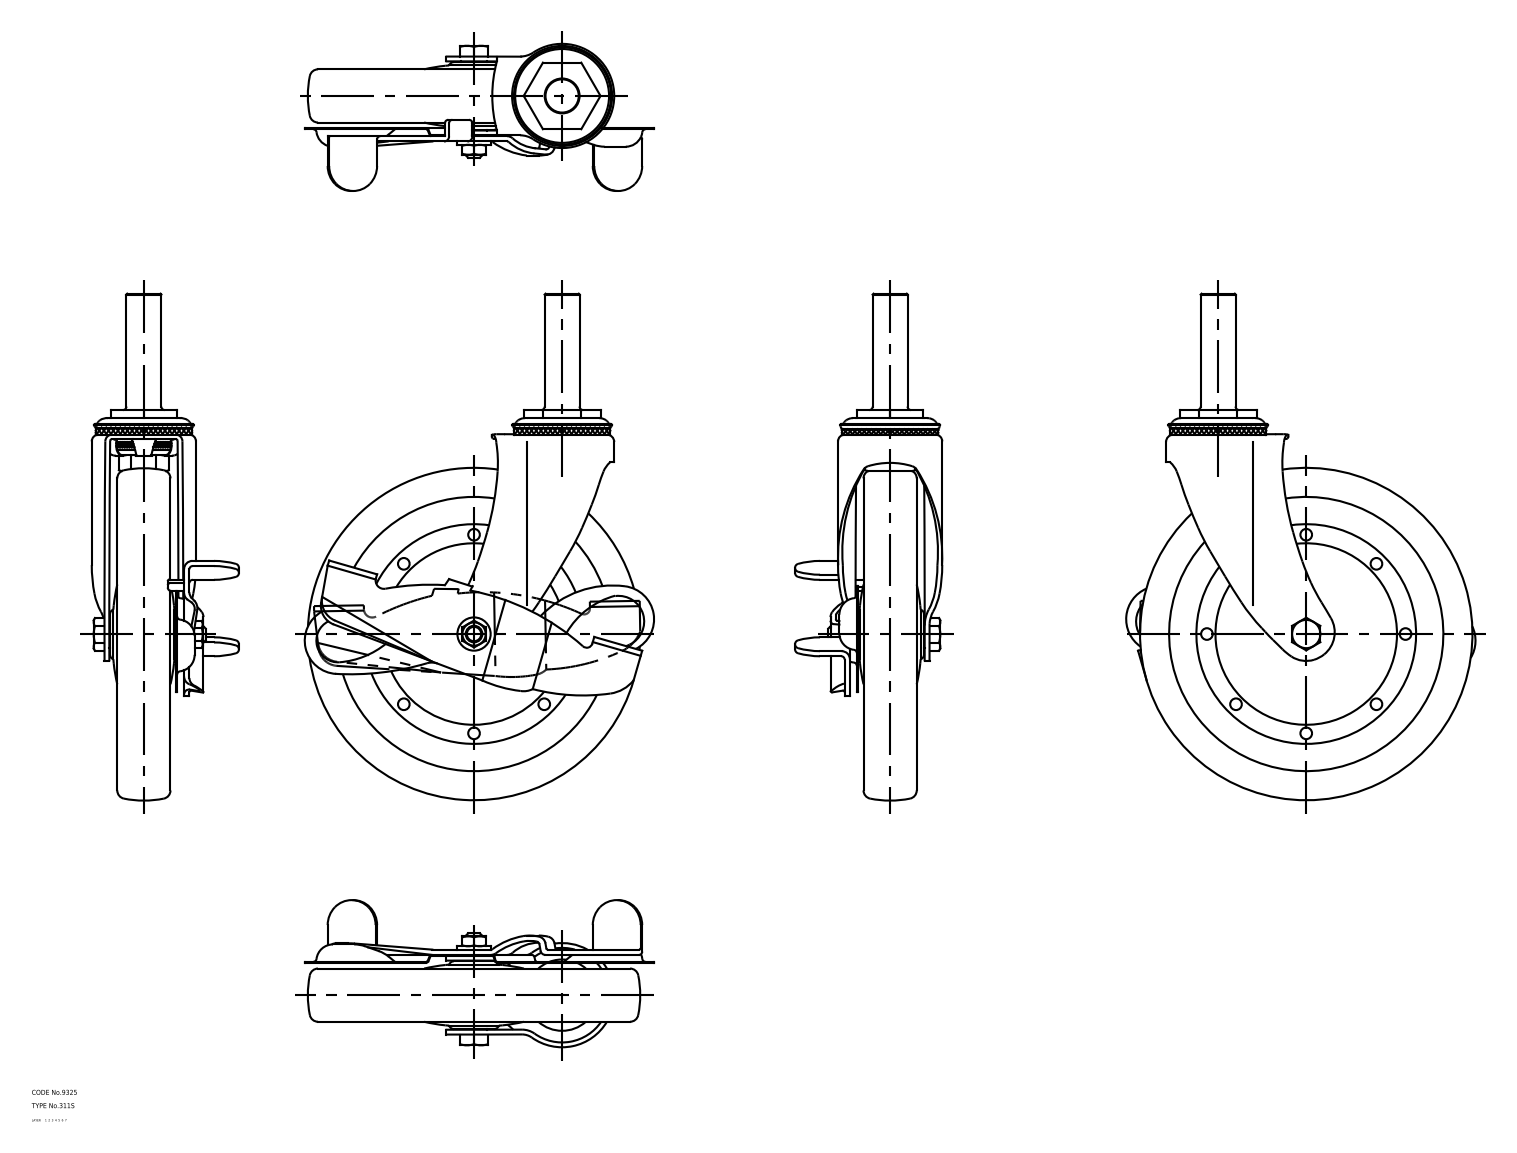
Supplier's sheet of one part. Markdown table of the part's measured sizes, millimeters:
| quantity | value |
| --- | --- |
| part name | 67146639; 67146652; 67146665; 67146678 (+2 more) |
| STEP written by | CADfix (AUTOMOTIVE_DESIGN) |
| units | millimeters |
| bodies | 6 solids, 540 faces (0 planar, 0 cylindrical, 540 other) |
| overall size | 305 × 210.18 × 88.55 |
| volume | 962 230 mm³ |
| surface area | 184 076 mm² |
